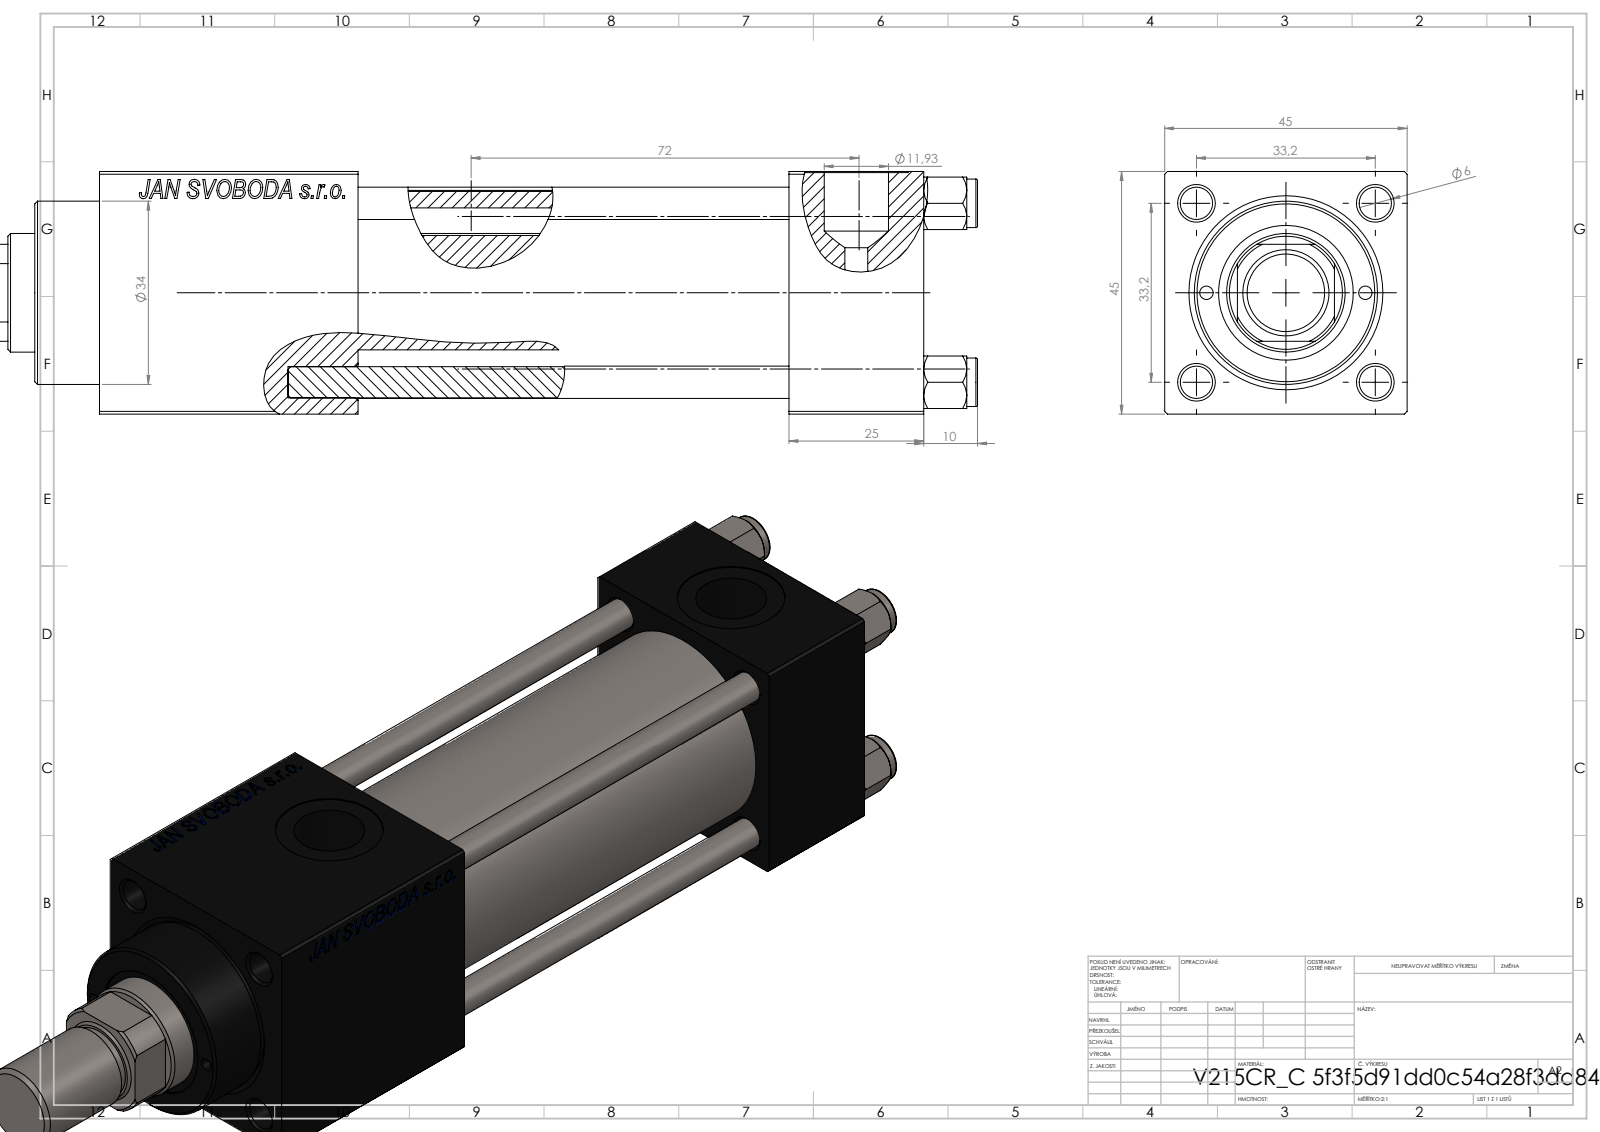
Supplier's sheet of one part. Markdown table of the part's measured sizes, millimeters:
| quantity | value |
| --- | --- |
| part name | NUT_M5_C; V215CR_C_Body; V215CR_C_TYCINKA; ROD_END_AH (+2 more) |
| STEP written by | SolidWorks 2019 (CONFIG_CONTROL_DESIGN) |
| units | millimeters |
| bodies | 12 solids, 1168 faces (531 planar, 95 cylindrical, 542 other) |
| overall size | 210 × 45 × 45 |
| volume | 238 615 mm³ |
| surface area | 84 044 mm² |
| round holes (diameter × count) | 6 × 4, 2.5 × 2, 7 × 2, 13.16 × 2, 20 × 2, 10.5 × 1, 22 × 1, 24 × 1, 25 × 1, 32 × 1, 33 × 1 |
| round bosses / shafts (diameter × count) | 9 × 4, 38 × 1, 34 × 1, 16 × 1, 14 × 1 |
| partial cylindrical surfaces (radius × count) | 10.5 × 1 |
| main face-to-face distances | 45, 25, 153, 105, 80, 128, 48, 124.3, 99.3, 19.3 |
| hole center spacings | 16.7, 23.48, 33.2, 35.47, 14.75, 46.95, 29.5, 105.5 |
